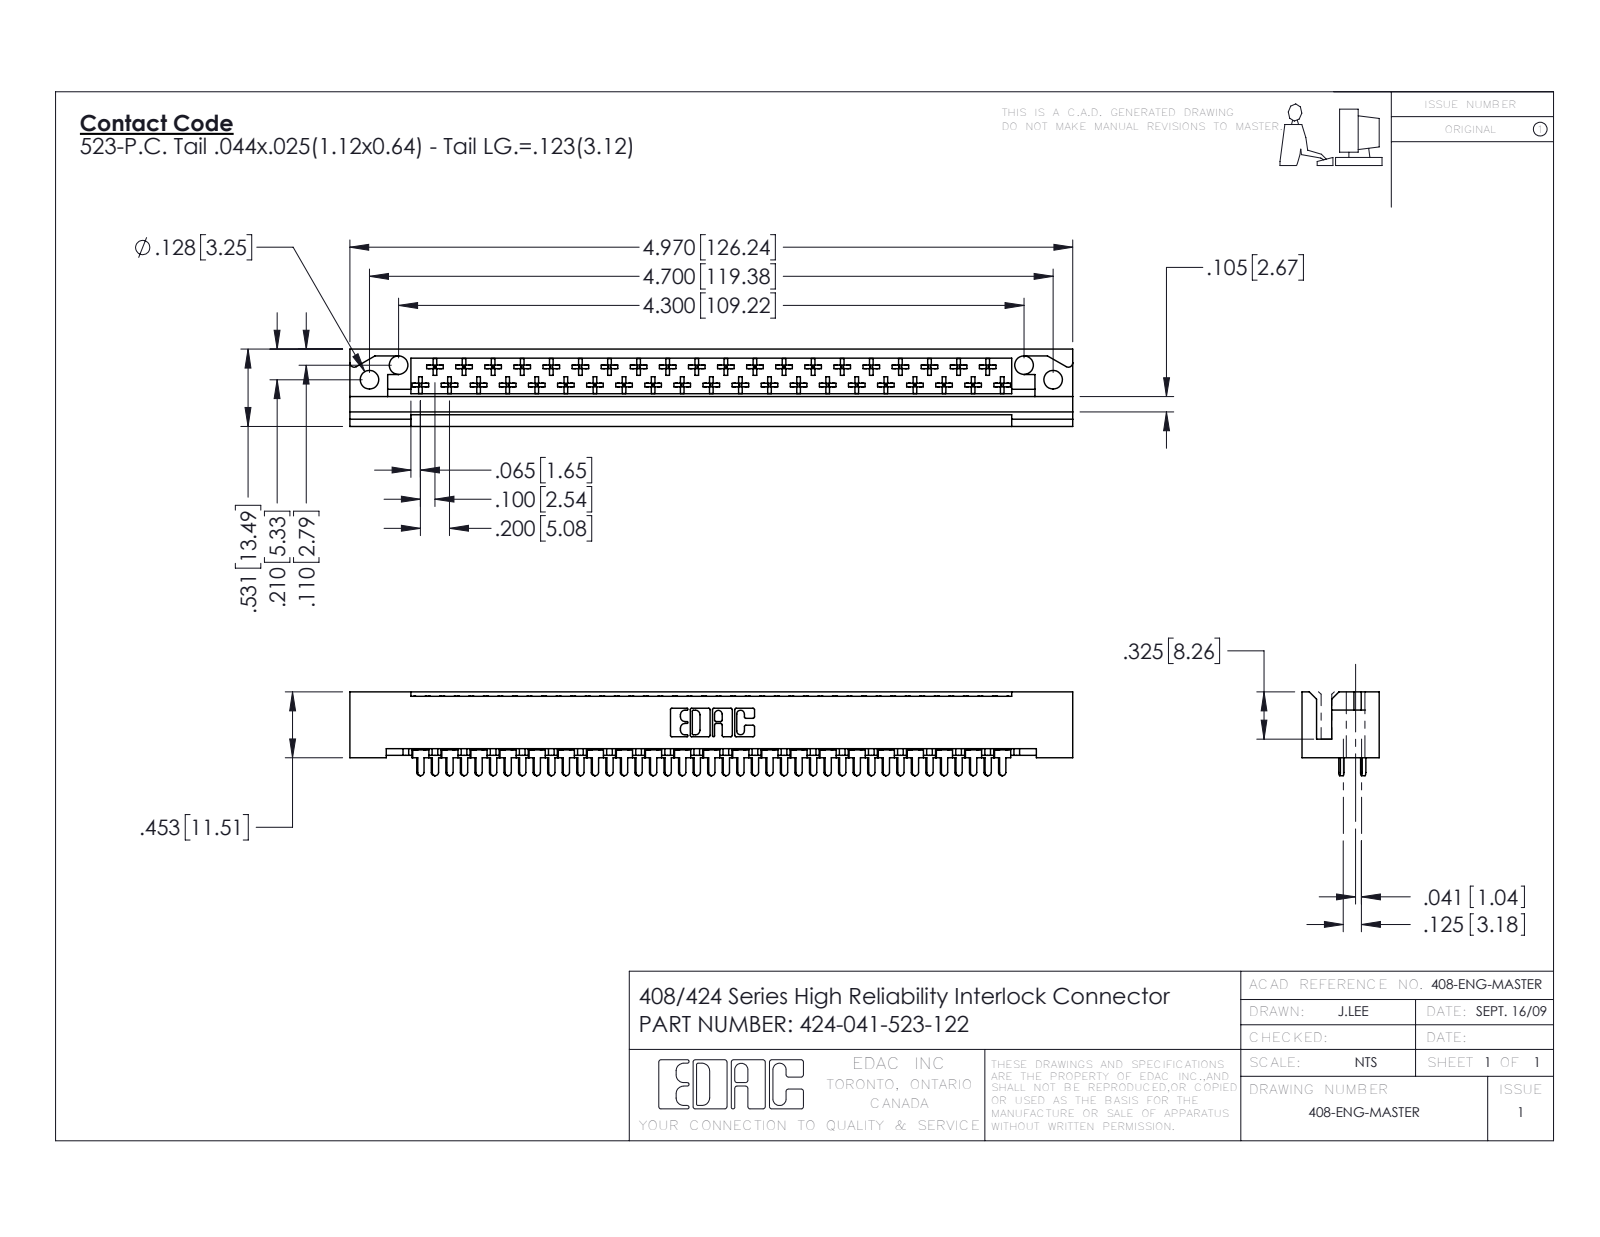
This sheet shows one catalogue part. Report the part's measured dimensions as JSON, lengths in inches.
{"part_name": "424-047-523-122; 424 Part_041; 408-290-001_408-290-123 - Bottom; 408-290-001_408-290-123 - Top", "step_written_by": "SolidWorks 2016 (CONFIG_CONTROL_DESIGN)", "units": "inches", "bodies": {"solids": 42, "faces": 2400, "planar": 1811, "cylindrical": 425, "other": 164}, "overall_size": [4.97, 0.576, 0.531], "volume_in3": 0.796, "surface_area_in2": 26.52, "round_holes": [[0.128, 4]], "partial_cylinders_radius": [[0.01, 246], [0.02, 43], [0.022, 41], [0.01, 22], [0.007, 6], [0.031, 6], [0.026, 3], [0.03, 2]], "face_to_face_distances": [0.1, 0.296, 0.025, 0.531, 0.125, 0.272, 0.235, 0.259, 0.025, 0.217], "hole_center_spacings": [0.224, 4.501, 4.3, 4.7]}
